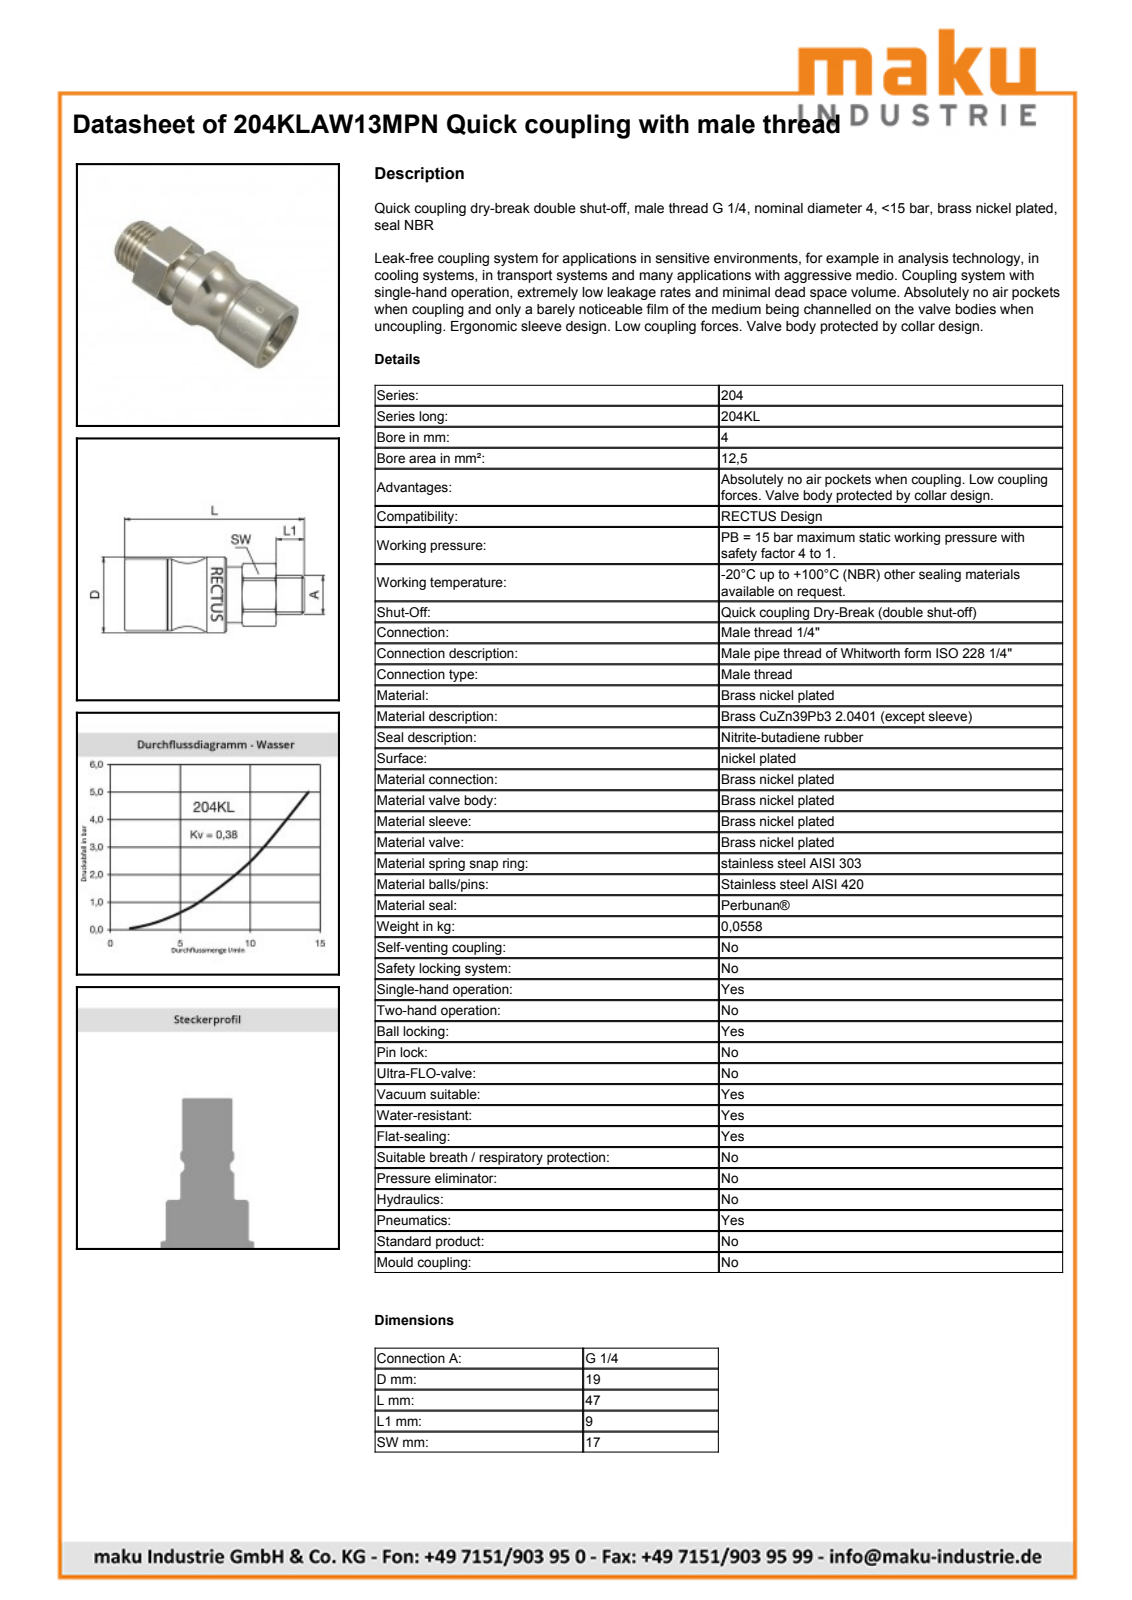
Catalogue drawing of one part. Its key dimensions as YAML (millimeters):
part_name: "D112147"
step_written_by: "Autodesk Inventor 2013 (AUTOMOTIVE_DESIGN)"
units: millimeters
bodies: {solids: 1, faces: 865, planar: 361, cylindrical: 113, other: 391}
overall_size: [46.83, 19.08, 19]
volume: 8988
surface_area: 6355
round_holes:
  - {diameter: 10.45, count: 1}
  - {diameter: 11.46, count: 1}
  - {diameter: 12.7, count: 1}
  - {diameter: 14.05, count: 1}
  - {diameter: 14.2, count: 1}
  - {diameter: 14.6, count: 1}
  - {diameter: 17, count: 1}
  - {diameter: 17.2, count: 1}
round_bosses_or_shafts:
  - {diameter: 19, count: 1}
  - {diameter: 18, count: 1}
  - {diameter: 16.35, count: 1}
  - {diameter: 14.8, count: 1}
  - {diameter: 14, count: 1}
  - {diameter: 13.16, count: 1}
  - {diameter: 13, count: 1}
  - {diameter: 12.5, count: 1}
partial_cylinders:
  - {radius: 8.9, count: 1}
  - {radius: 9.4, count: 1}
  - {radius: 9.57, count: 1}
face_to_face_distances: [17, 9, 46.83, 37.83, 25.55, 12.28, 21.28, 2.5, 23.05, 29.28]
